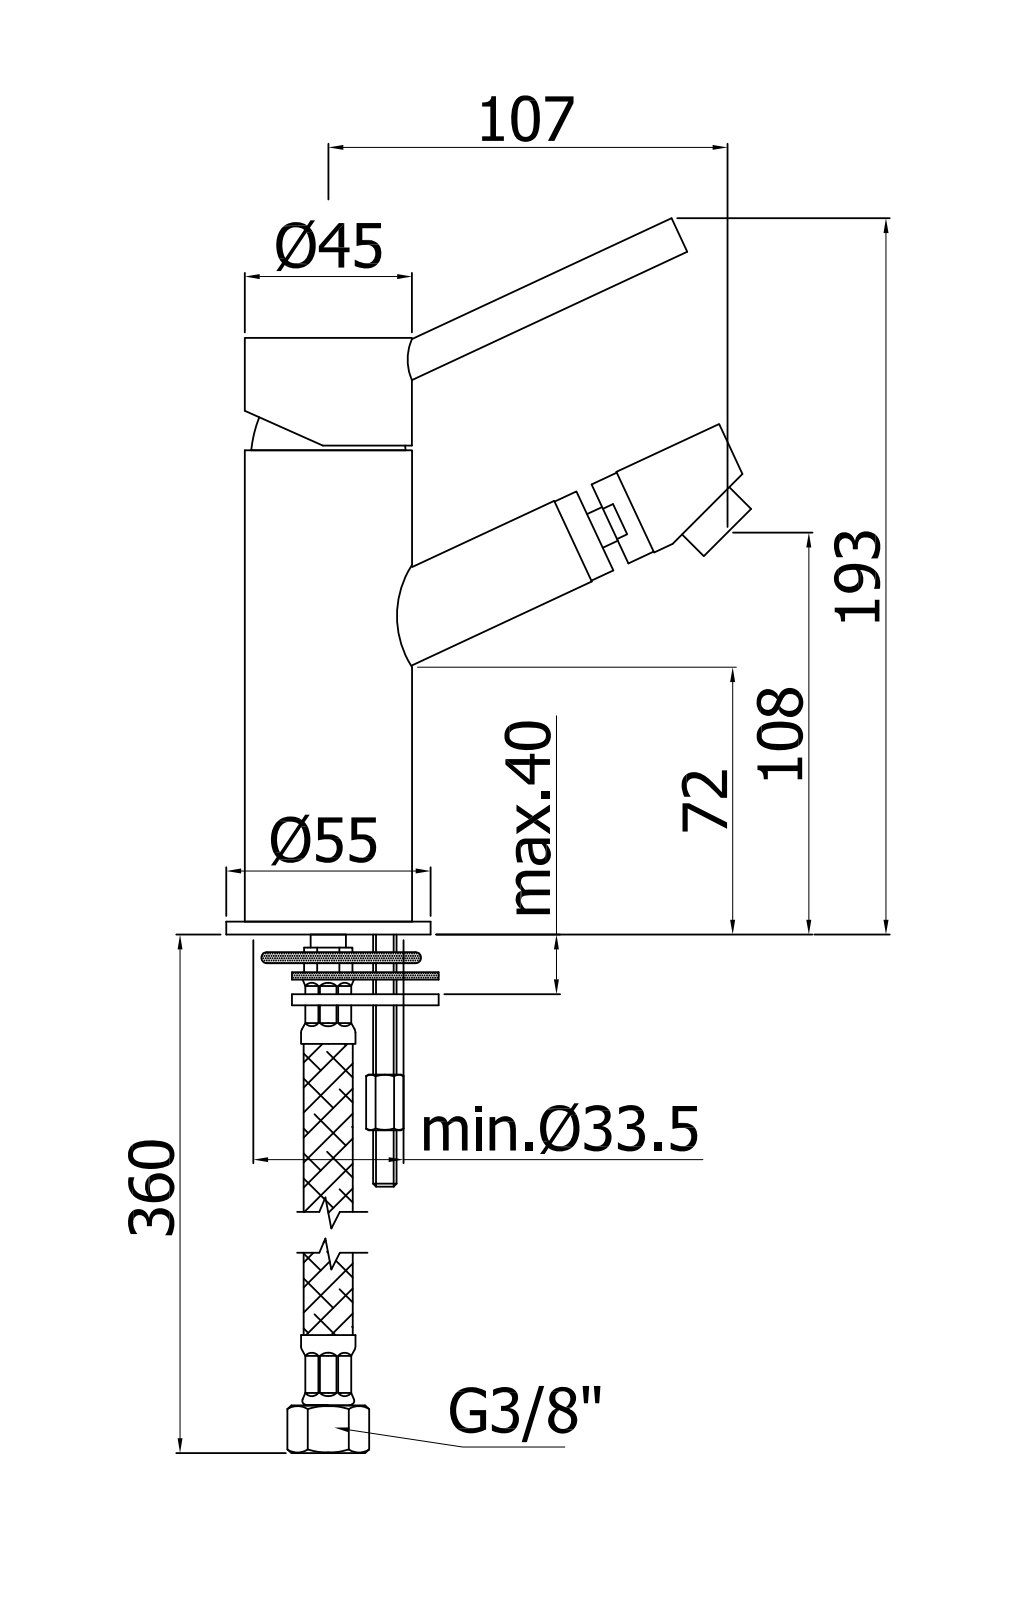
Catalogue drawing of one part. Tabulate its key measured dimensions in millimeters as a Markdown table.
| quantity | value |
| --- | --- |
| part name | BI131CR |
| STEP written by | CREO PARAMETRIC BY PTC INC, 2020044 (CONFIG_CONTROL_DESIGN) |
| units | millimeters |
| bodies | 1 solid, 1061 faces (592 planar, 256 cylindrical, 213 other) |
| overall size | 192.84 × 143.06 × 55 |
| volume | 231 488 mm³ |
| surface area | 72 444 mm² |
| round holes (diameter × count) | 11 × 3, 4 × 2, 6.5 × 2, 9 × 2, 3.3 × 1, 4.5 × 1, 5 × 1, 6.8 × 1, 10 × 1, 15.5 × 1, 18.2 × 1, 19.5 × 1 |
| round bosses / shafts (diameter × count) | 25 × 2, 55 × 1, 45 × 1, 40 × 1, 37 × 1, 35 × 1, 34.8 × 1, 32.2 × 1 |
| partial cylindrical surfaces (radius × count) | 0.5 × 51, 0.15 × 11, 0.3 × 4, 1 × 2, 3 × 1, 5 × 1, 7 × 1, 9.3 × 1 |
| main face-to-face distances | 26.5, 132.1, 3.5, 4.5, 5.5, 121.5, 104.3, 100.8, 23, 77.8 |
| hole center spacings | 3.54, 8.06, 8.75, 10.97, 14.01, 15.89, 12.5, 15 |
